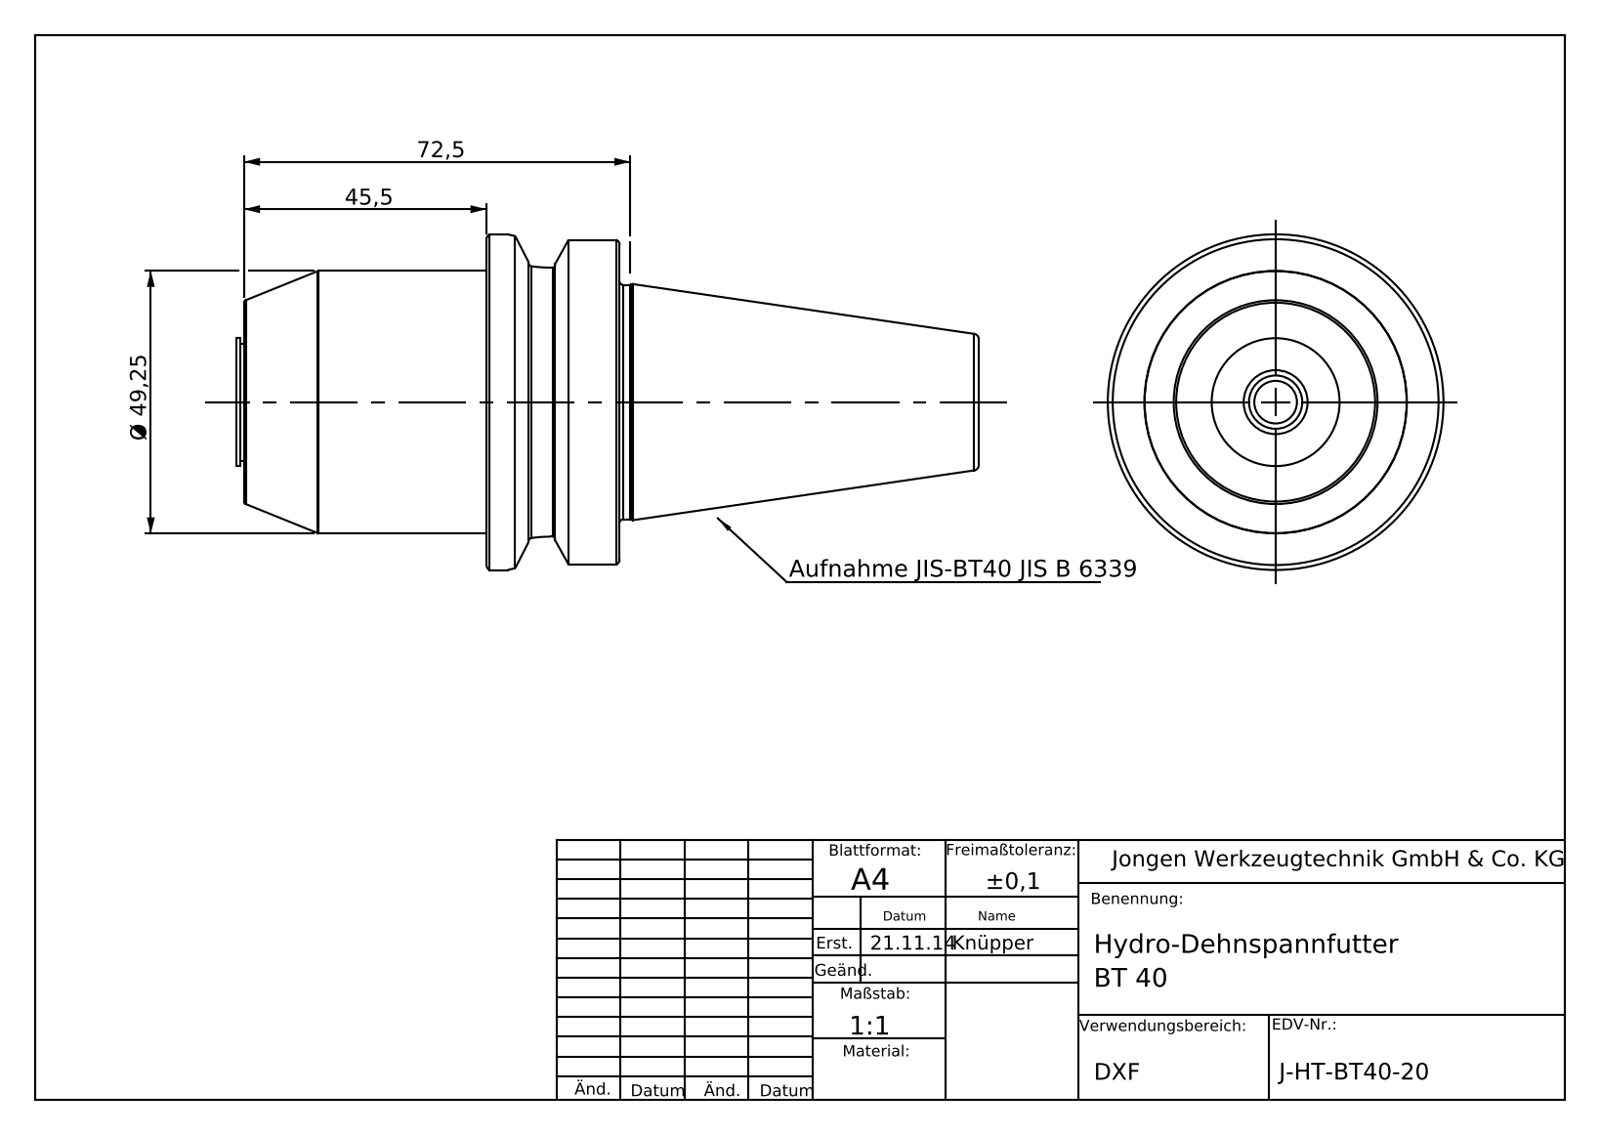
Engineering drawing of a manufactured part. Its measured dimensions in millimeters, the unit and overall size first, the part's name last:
Units: millimetres
Overall size (bounding box): 137.9 × 62.98 × 62.98
Round holes (diameter × count): ⌀3.2 ×4, ⌀4 ×4, ⌀14 ×1, ⌀17.01 ×1, ⌀20 ×1, ⌀20.35 ×1, ⌀25.4 ×1
Round bosses / shafts (diameter × count): ⌀62.98 ×1, ⌀53 ×1, ⌀49.25 ×1, ⌀44.45 ×1, ⌀24.4 ×1, ⌀22.1 ×1
Partial cylindrical surfaces — rounded edges, fillets, slot ends (radius × count): R0.1 ×4, R8.1 ×1
Main face-to-face distances: 25, 70.5, 45.5, 45, 18, 7, 52.5, 16.2, 10, 27
Hole centre spacings: 29.9
Volume: 181 138 mm³ · Surface area: 38 523 mm²
Bodies: 1 solid, 155 faces (31 planar, 62 cylindrical, 62 other)
Part name (STEP PRODUCT): J-HT-BT40-20
STEP written by: SolidWorks 2017 (AUTOMOTIVE_DESIGN)
